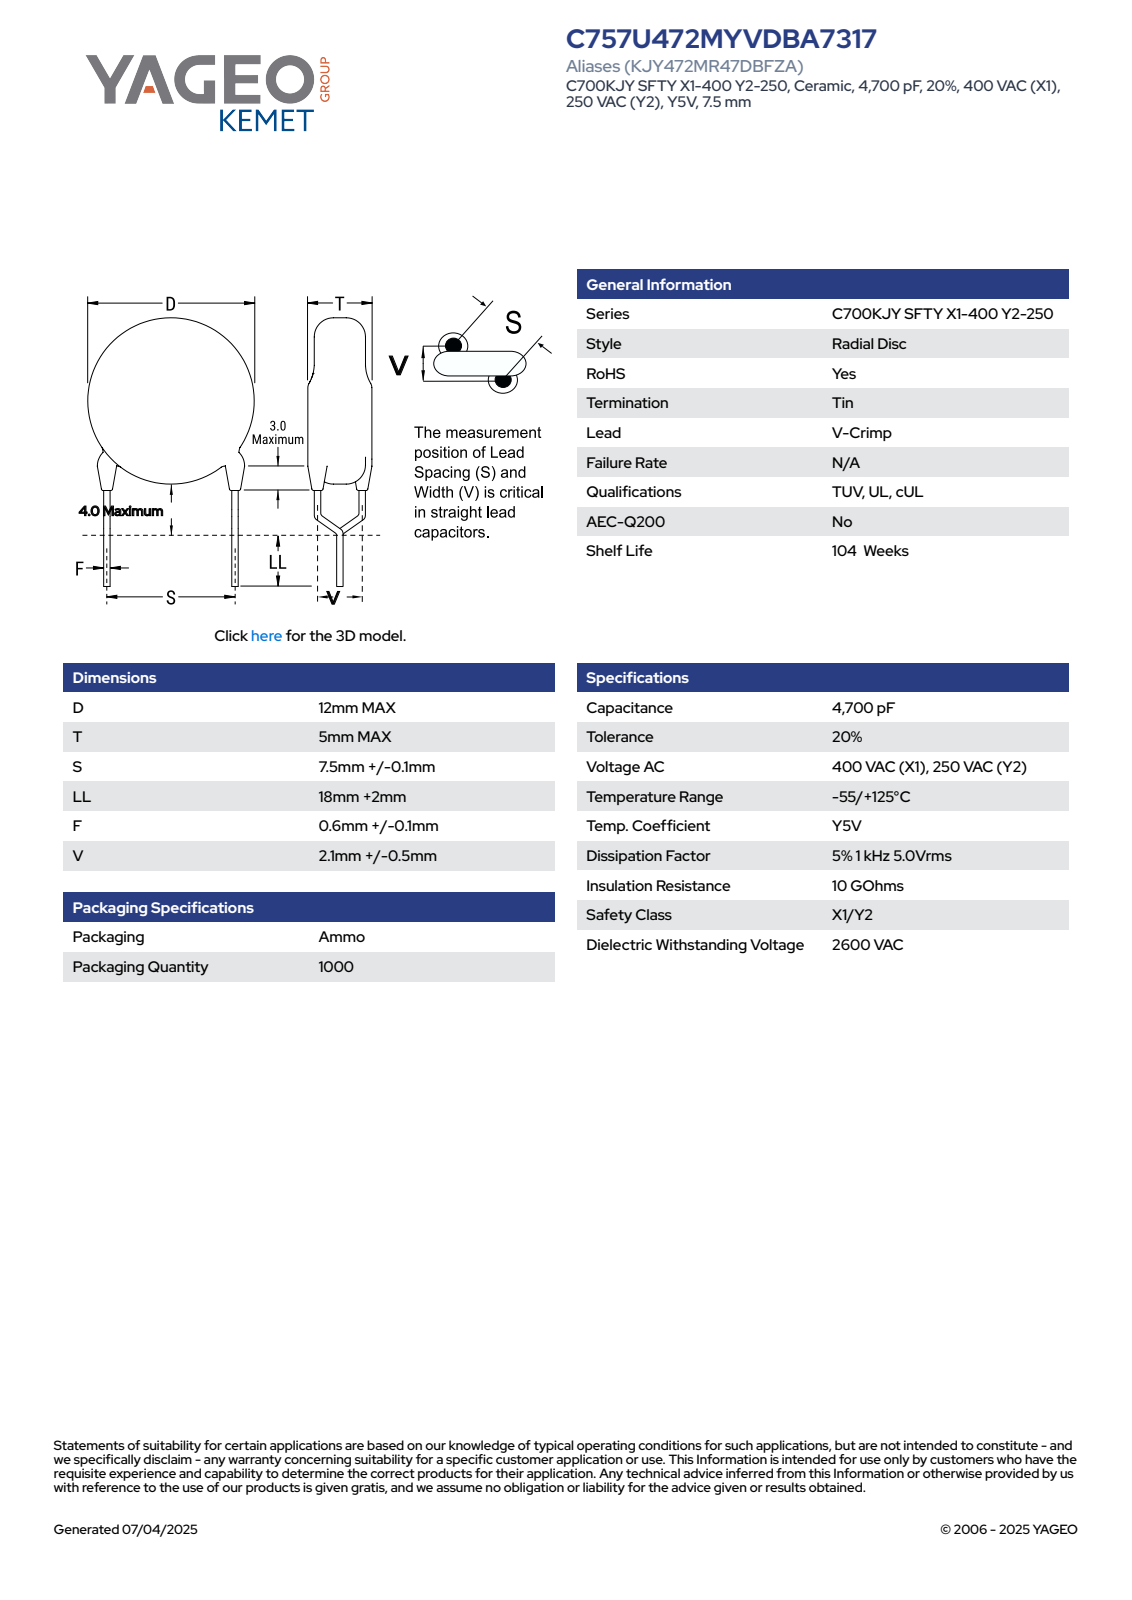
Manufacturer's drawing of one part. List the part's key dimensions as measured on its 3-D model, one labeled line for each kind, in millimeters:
Part name (STEP PRODUCT): CCD_VC12X5_D12T5S7.5LL20F0.7V2.1
STEP written by: SolidWorks 2021 (AUTOMOTIVE_DESIGN)
Units: millimetres
Bodies: 4 solids, 85 faces (63 planar, 18 cylindrical, 4 other)
Overall size (bounding box): 32 × 12.16 × 5
Volume: 569 mm³ · Surface area: 504 mm²
Round bosses / shafts (diameter × count): ⌀0.7 ×6, ⌀1.2 ×2, ⌀12 ×1
Main face-to-face distances: 5, 20, 27.43, 7.43, 25.5, 5.5, 1.93, 0.53, 0.36, 7.93
